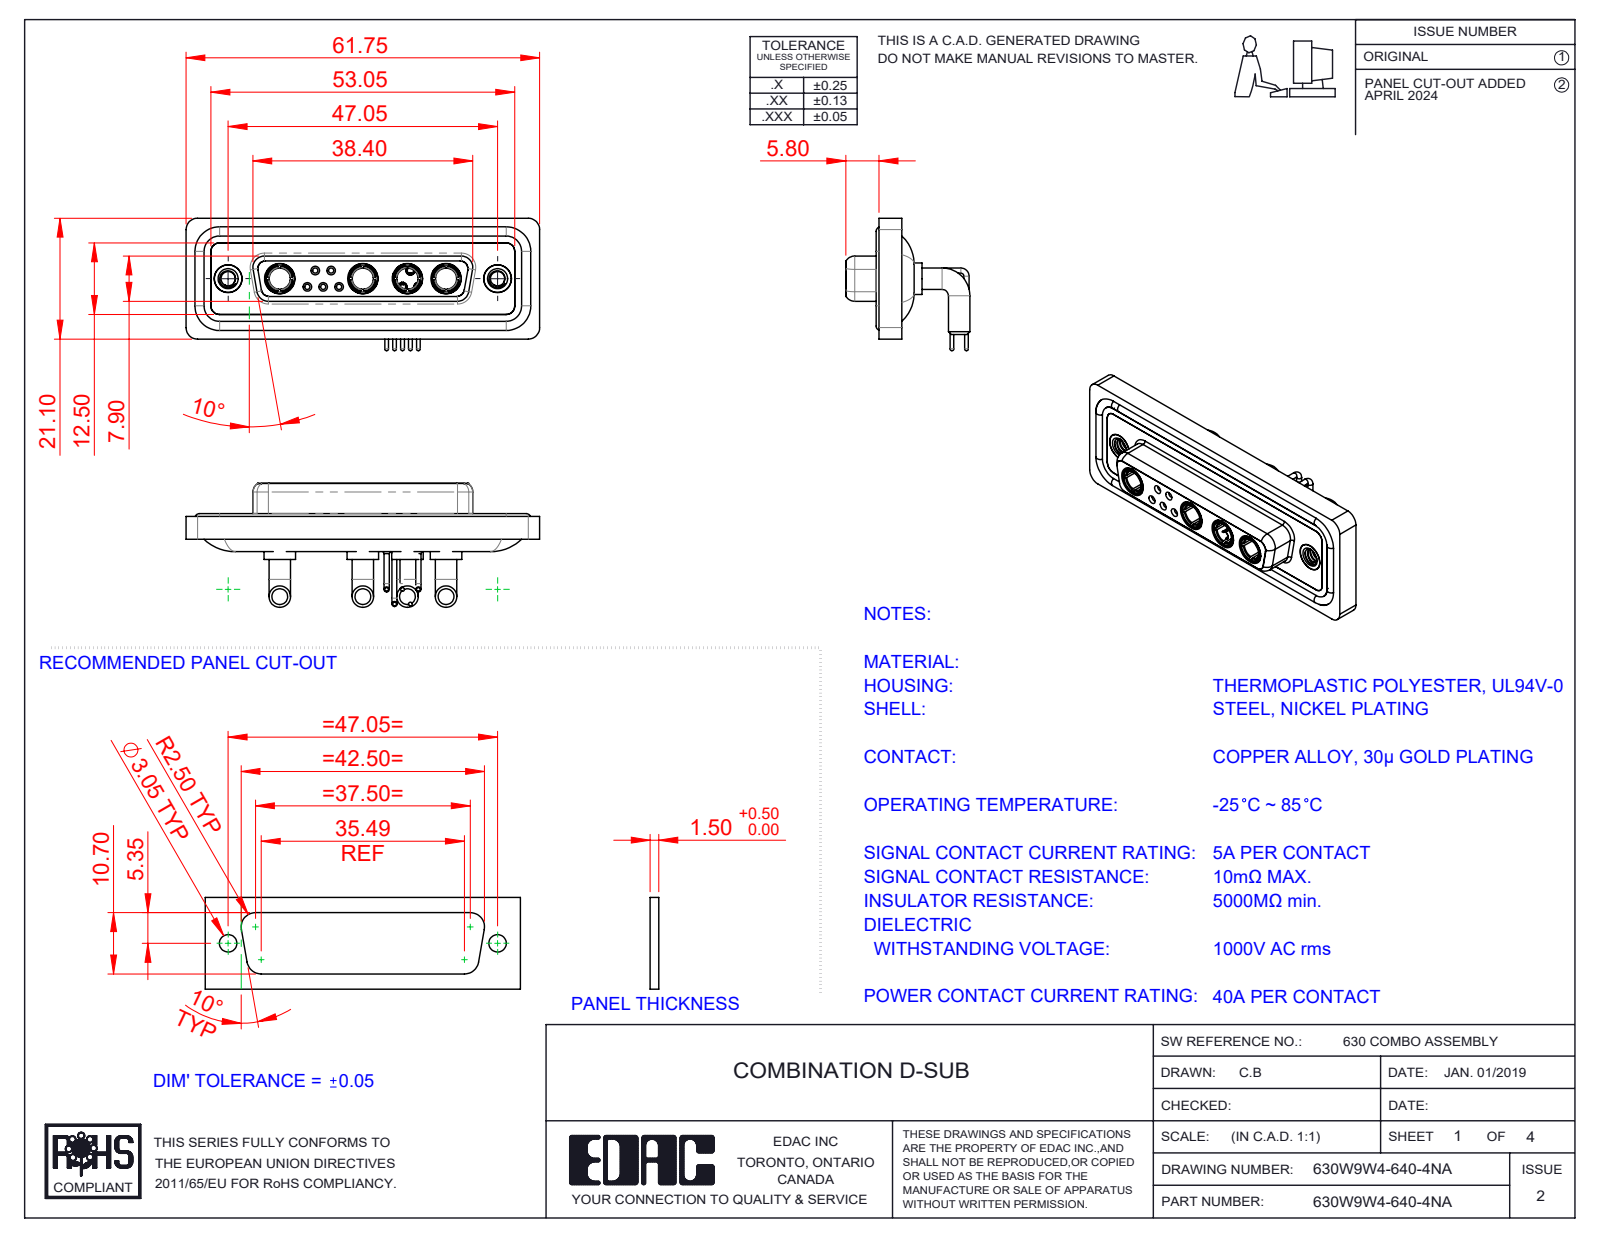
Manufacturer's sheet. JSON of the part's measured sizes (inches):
{"part_name": "630Combo Waterproof Housing_25 Contacts; 630Combo Shell Rear_25 Contacts; 630Combo Housing_9W4; 630W9W4-640-4NA (+5 more)", "step_written_by": "SolidWorks 2023 (CONFIG_CONTROL_DESIGN)", "units": "inches", "bodies": {"solids": 20, "faces": 957, "planar": 296, "cylindrical": 401, "other": 260}, "overall_size": [2.431, 0.91, 0.854], "volume_in3": 0.533, "surface_area_in2": 22.05, "round_holes": [[0.191, 6], [0.035, 5], [0.043, 5], [0.059, 5], [0.079, 5], [0.146, 4], [0.209, 4], [0.063, 3], [0.067, 2], [0.098, 2], [0.157, 2], [0.159, 2]], "round_bosses_or_shafts": [[0.035, 10], [0.063, 9], [0.148, 8], [0.079, 5], [0.059, 5], [0.026, 5], [0.217, 4], [0.205, 4]], "partial_cylinders_radius": [[0.059, 18], [0.079, 18], [0.053, 8], [0.063, 8], [0.01, 4], [0.02, 4], [0.024, 4], [0.026, 4]], "face_to_face_distances": [0.016, 0.071, 0.161, 0.043, 0.063, 0.098, 0.122, 0.146, 0.059, 0.055], "hole_center_spacings": [0.124, 0.109, 0.198, 0.545, 0.436, 0.504, 0.61, 0.218]}
